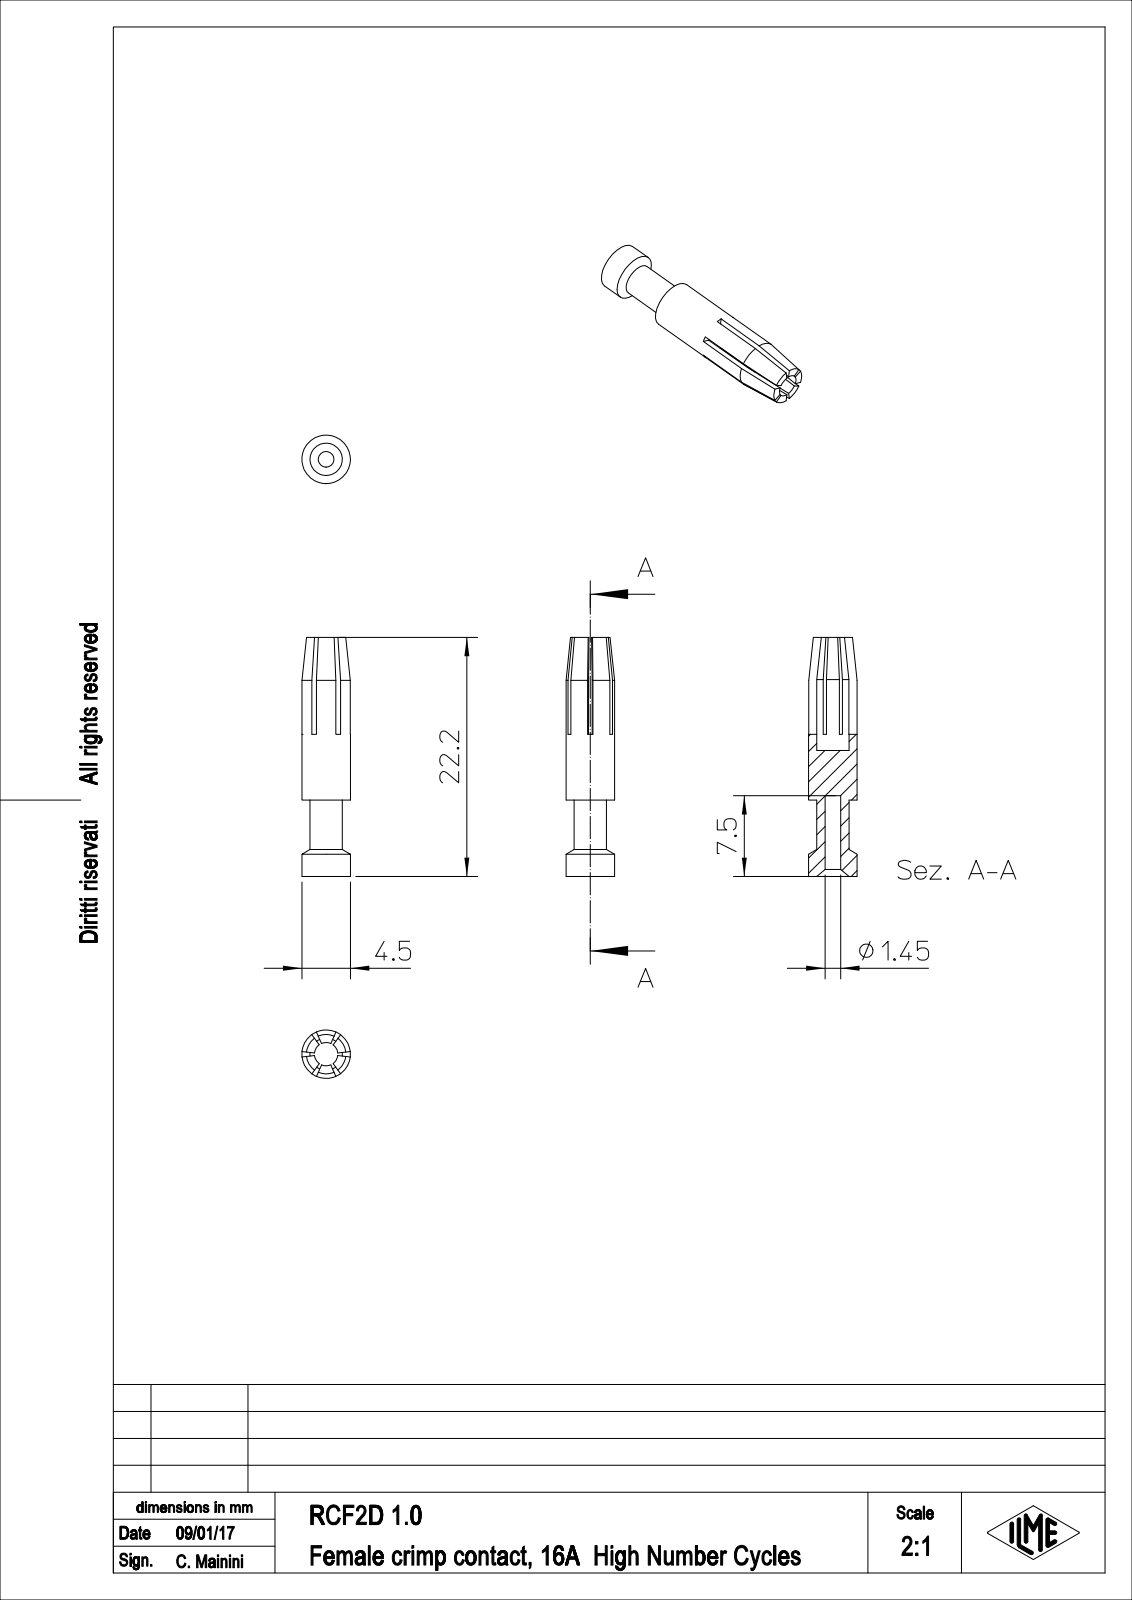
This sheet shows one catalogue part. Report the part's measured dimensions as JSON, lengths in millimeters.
{"part_name": "RCF2D_1.0", "step_written_by": "PTC Creo Elements/Direct Modeling 19.0E 27-Jun-2016 (C) Parametric Technology GmbH (AUTOMOTIVE_DESIGN)", "units": "millimeters", "bodies": {"solids": 1, "faces": 54, "planar": 28, "cylindrical": 10, "other": 16}, "overall_size": [22.2, 4.5, 4.5], "volume_mm3": 202, "surface_area_mm2": 495, "round_holes": [[1.45, 1], [3, 1]], "round_bosses_or_shafts": [[4.5, 1]], "face_to_face_distances": [7.1, 4.6, 11.7, 10.5, 15.1, 22.2, 9, 1.5, 6.1, 13.2]}
